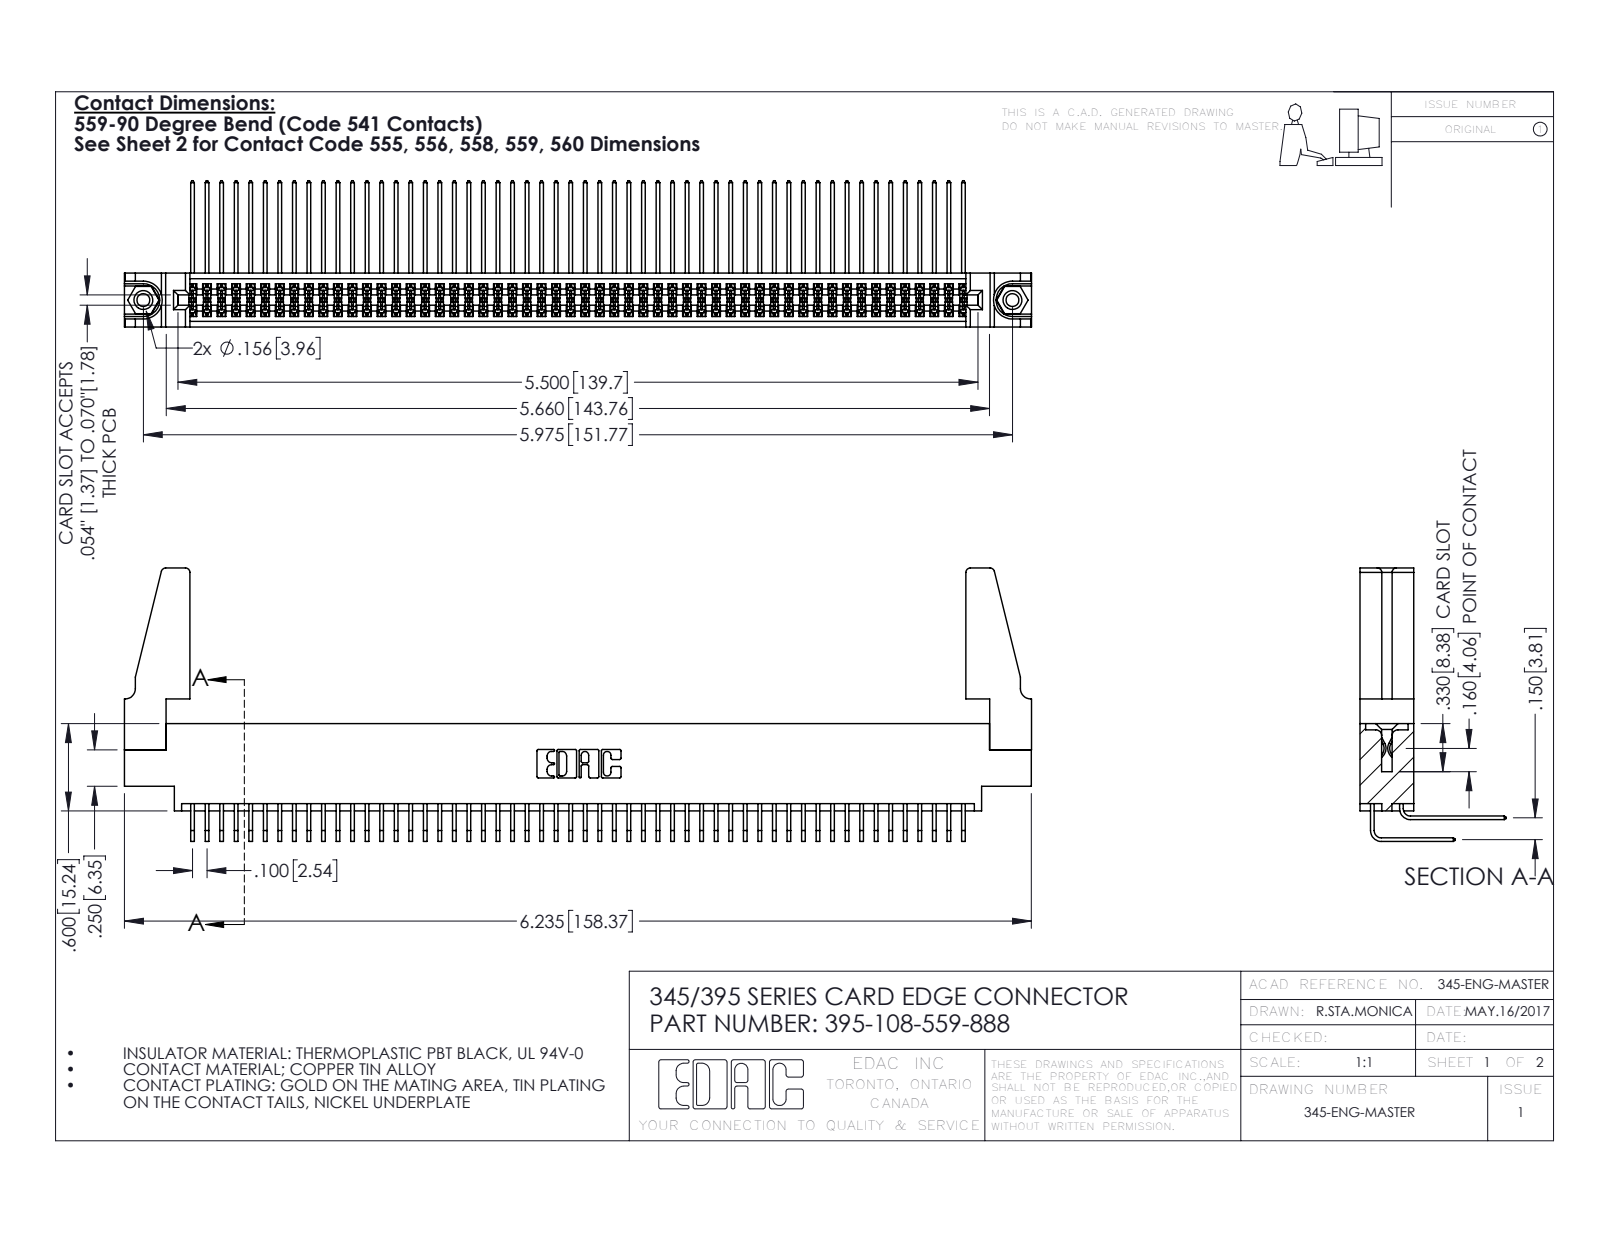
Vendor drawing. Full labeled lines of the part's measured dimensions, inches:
Part name (STEP PRODUCT): 395-108-559-888; 345-250-001_345-250-001-102; 345-220-078_345-220-088; 345-292-001_559 Tail - 2 (+2 more)
STEP written by: SolidWorks 2016 (CONFIG_CONTROL_DESIGN)
Units: inches
Bodies: 113 solids, 5870 faces (3936 planar, 1918 cylindrical, 16 other)
Overall size (bounding box): 6.236 × 1.879 × 1.005
Volume: 1.175 in³ · Surface area: 46.64 in²
Round holes (diameter × count): ⌀0.089 ×2, ⌀0.125 ×2, ⌀0.156 ×2, ⌀0.064 ×1
Round bosses / shafts (diameter × count): ⌀0.155 ×2
Partial cylindrical surfaces — rounded edges, fillets, slot ends (radius × count): R0.006 ×162, R0.01 ×22, R0.03 ×8, R0.007 ×6, R0.031 ×6, R0.026 ×3, R0.014 ×2, R0.019 ×2
Main face-to-face distances: 0.072, 0.298, 0.37, 0.2, 0.098, 0.272, 0.025, 0.225, 0.15, 0.175
Hole centre spacings: 0.27, 5.739, 5.975
